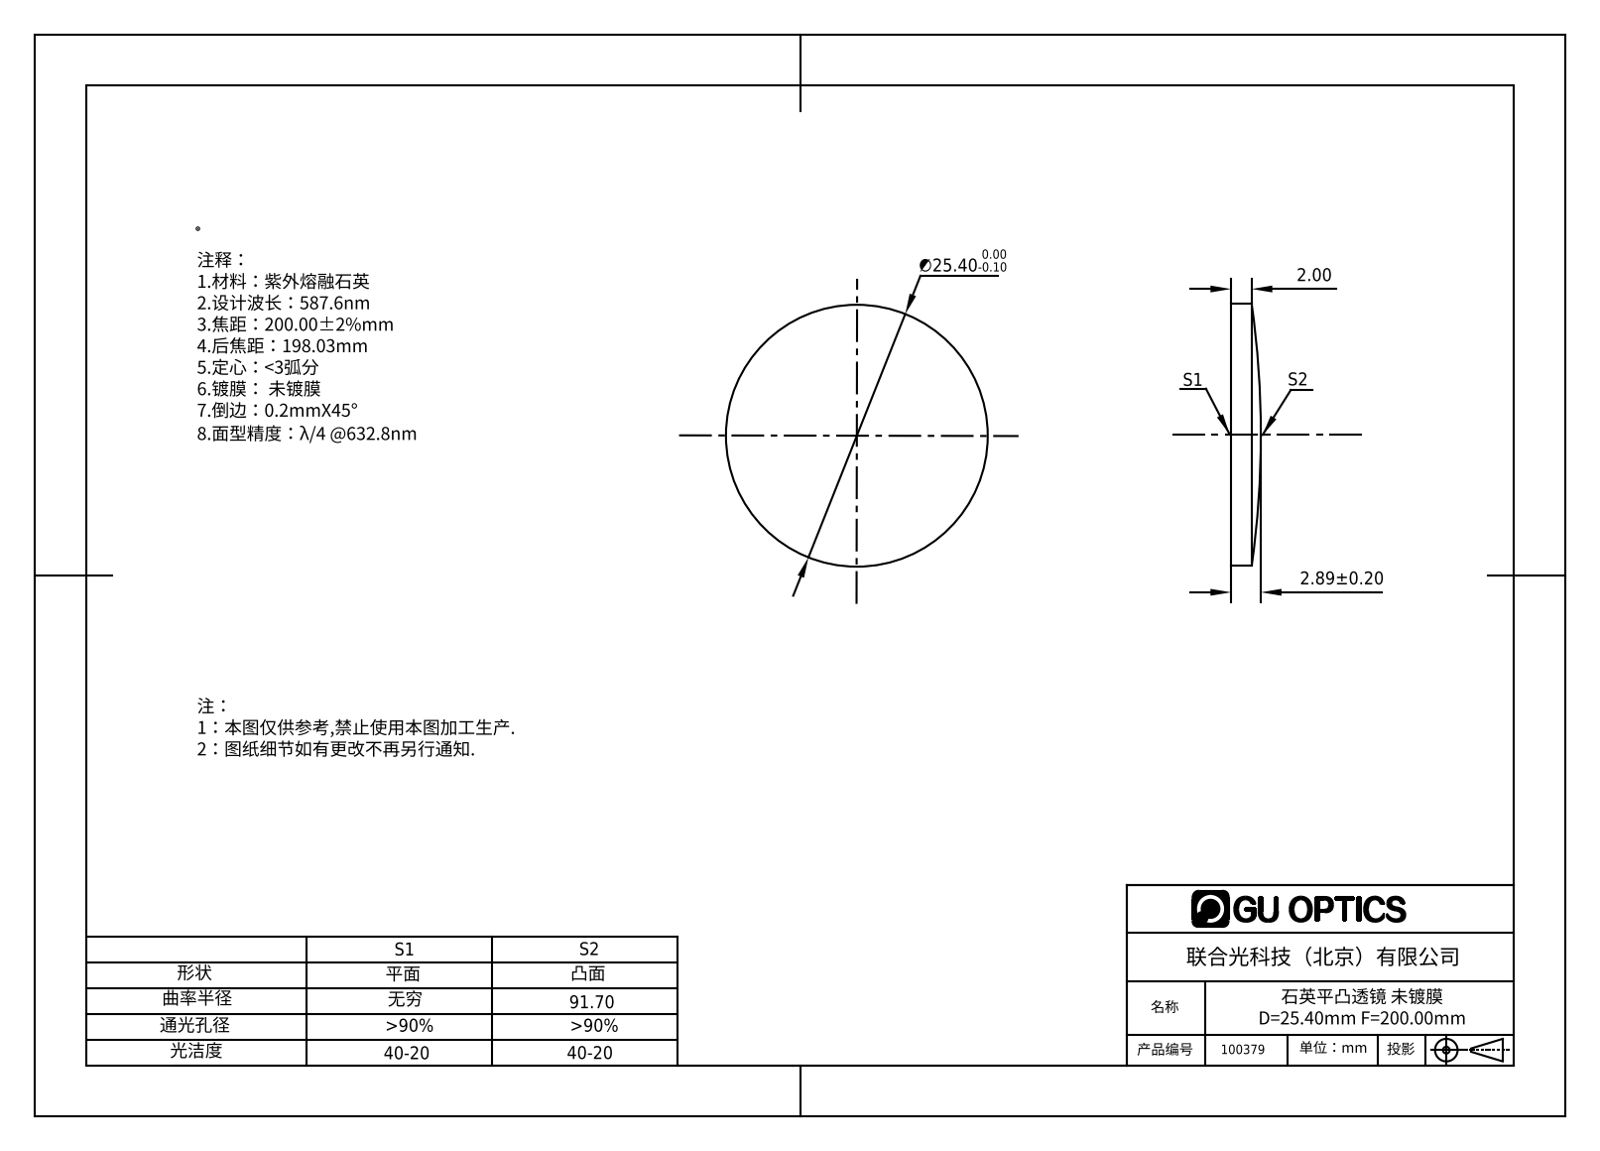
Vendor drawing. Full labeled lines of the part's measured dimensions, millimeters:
Part name (STEP PRODUCT): 100379
STEP written by: SolidWorks 2016 (AUTOMOTIVE_DESIGN)
Units: millimetres
Bodies: 1 solid, 5 faces (1 planar, 2 cylindrical, 2 other)
Overall size (bounding box): 25.4 × 25.4 × 2.89
Volume: 1 239 mm³ · Surface area: 1 176 mm²
Round bosses / shafts (diameter × count): ⌀25.4 ×1
